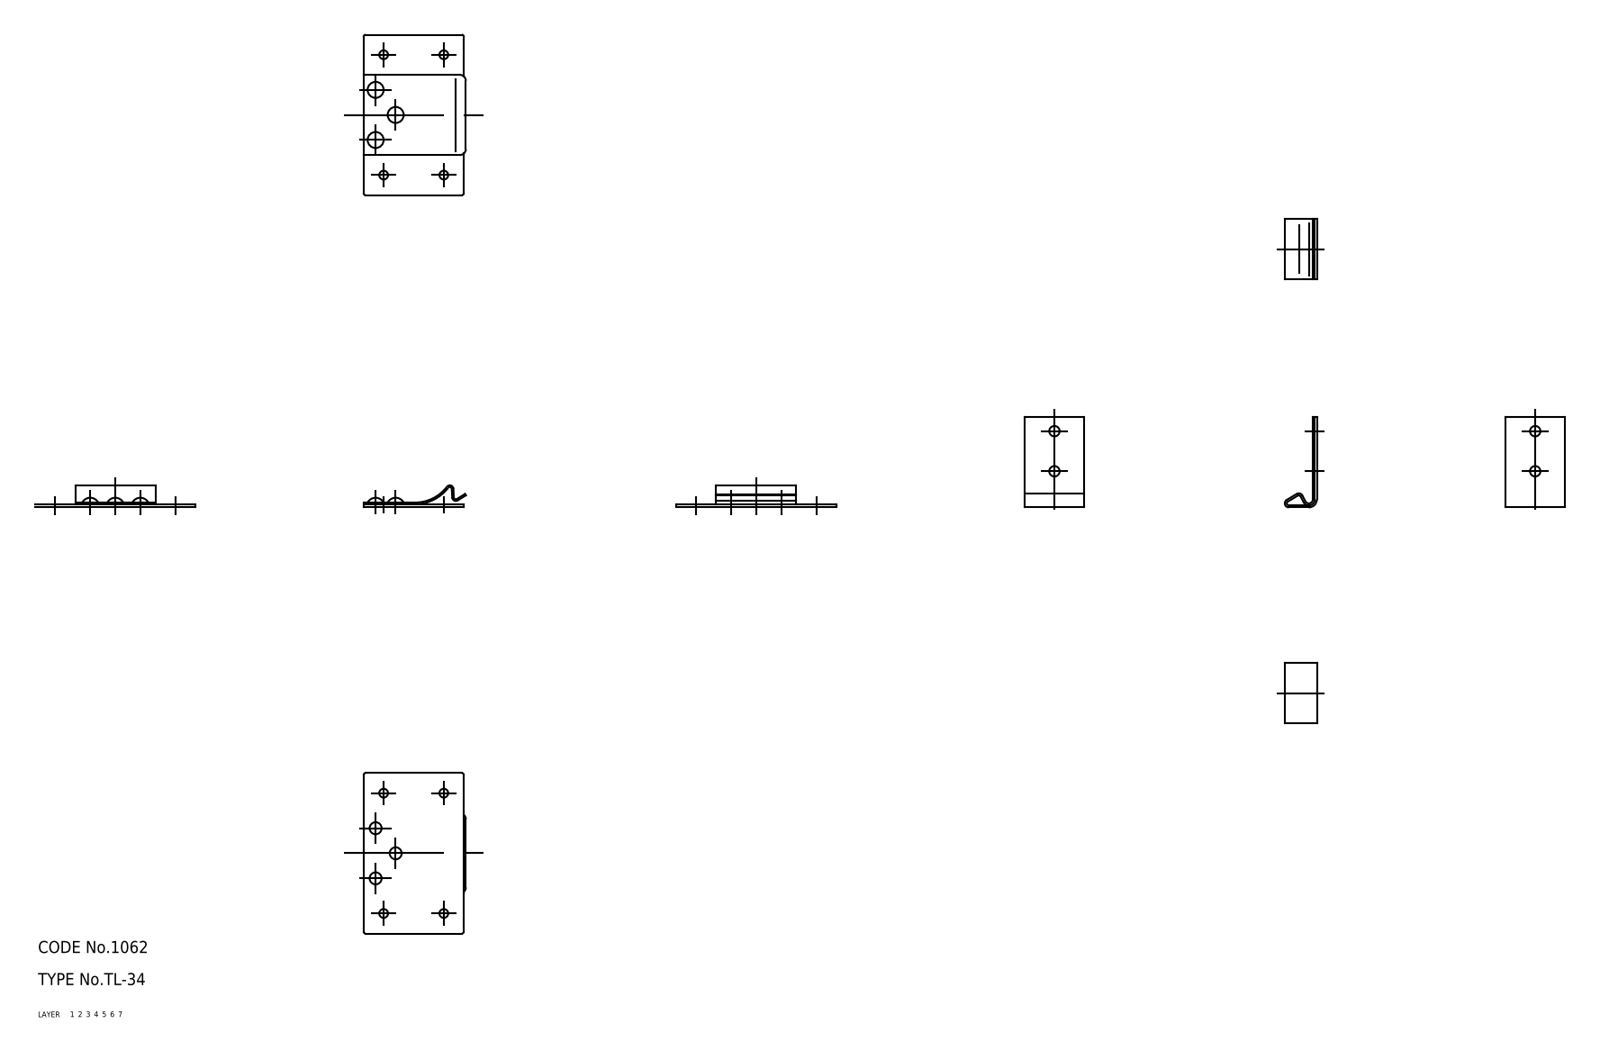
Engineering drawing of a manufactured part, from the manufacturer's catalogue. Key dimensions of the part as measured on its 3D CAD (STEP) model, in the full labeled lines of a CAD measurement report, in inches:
Part name (STEP PRODUCT): rivet; leaf spring; keeper; base (+1 more)
STEP written by: CADfix (AUTOMOTIVE_DESIGN)
Units: inches
Bodies: 6 solids, 93 faces (0 planar, 0 cylindrical, 93 other)
Overall size (bounding box): 2.618 × 1.575 × 0.917
Volume: 0.091 in³ · Surface area: 8.125 in²
